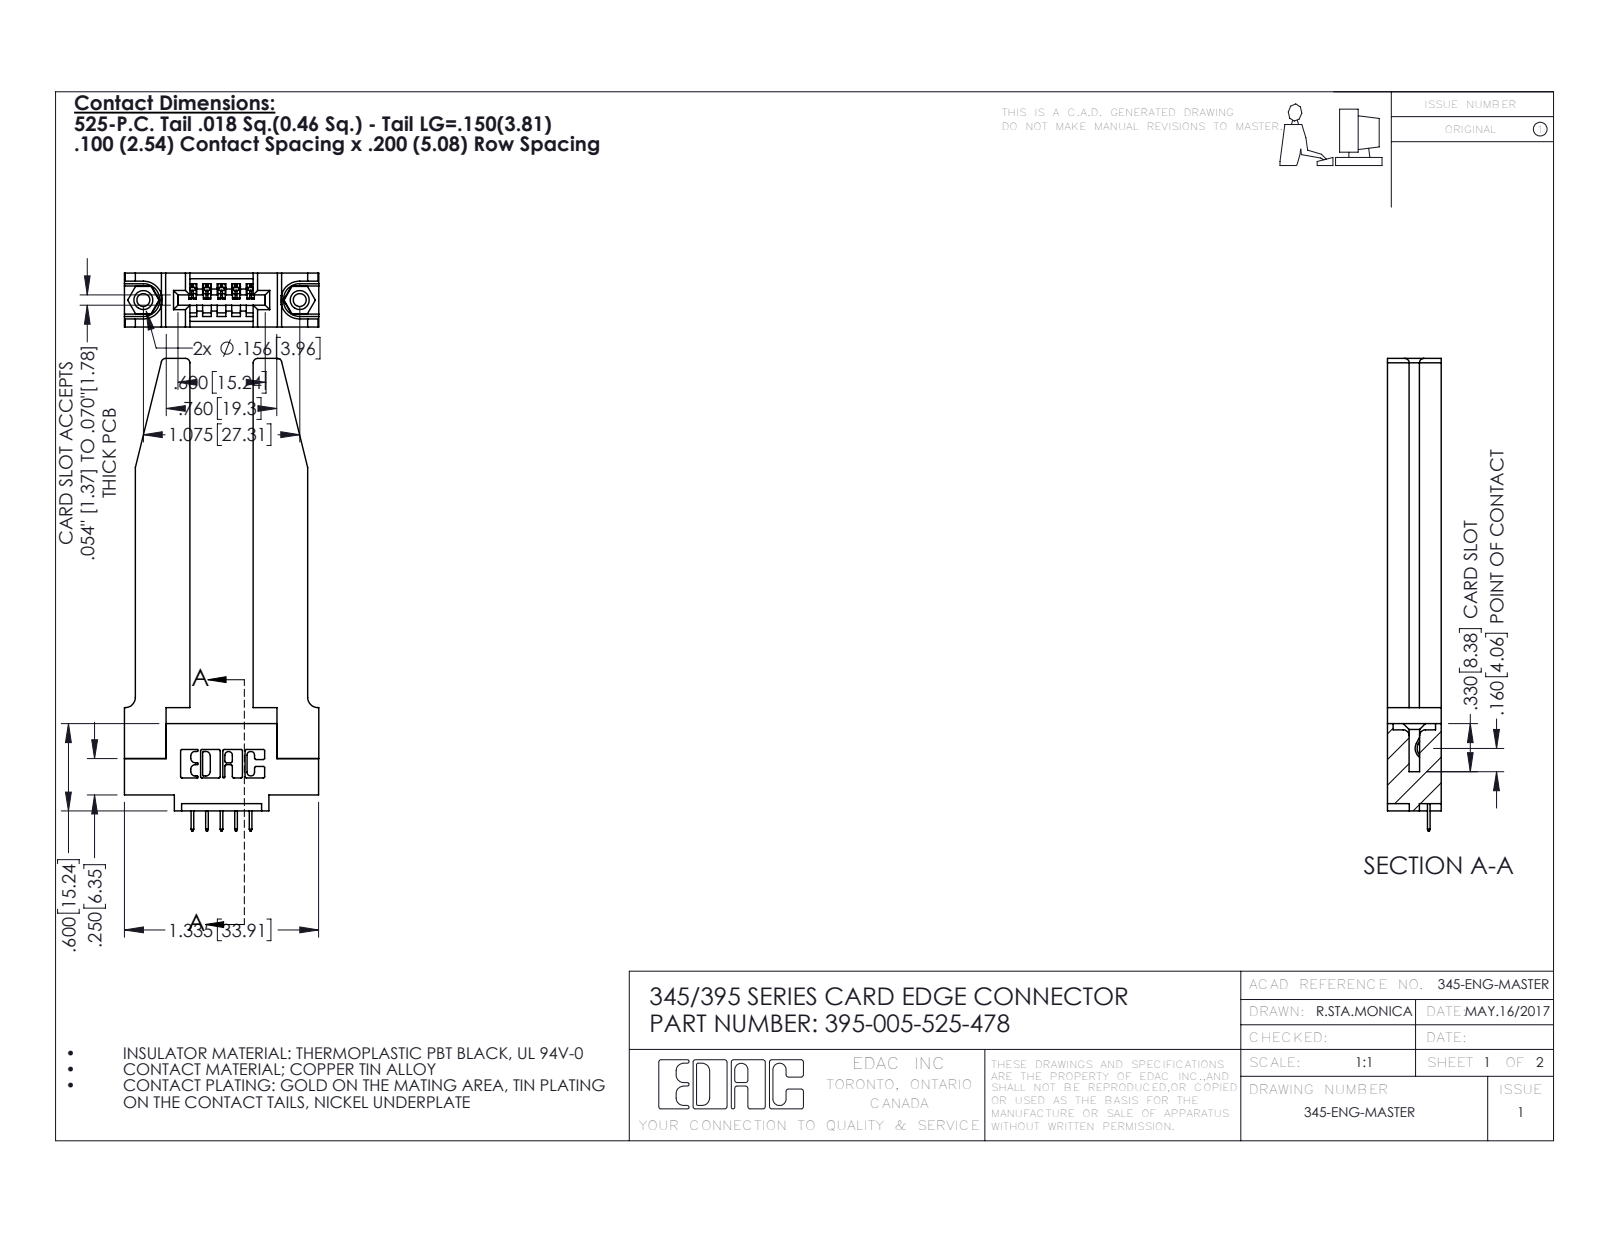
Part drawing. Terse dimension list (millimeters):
name: 345-292-001_345-293-125; 345 Part_0.110 Offset - 0.156 Dia-TH; 345-250-001_345-250-001-102; 345-220-078_345-220-078 (+1 more)
written by: SolidWorks 2020 (CONFIG_CONTROL_DESIGN)
unit: mm
bodies: 10 solids, 674 faces (456 planar, 166 cylindrical, 52 other)
size: 82.5 × 33.9 × 9.4
volume: 10 600 mm³; area: 10 110 mm²
holes: 2× ⌀2.3, 2× ⌀3.2, 2× ⌀4, 1× ⌀1.6
bosses: 2× ⌀3.9
rounds: 22× R0.3, 10× R0.2, 8× R0.8, 6× R0.2, 6× R0.8, 3× R0.7, 2× R0.8, 2× R1
face distances: 9.4, 3.8, 5.6, 11, 1.8, 3.8, 7.6, 2, 1.8, 1.4
hole spacings: 6.9, 21.5, 27.3
